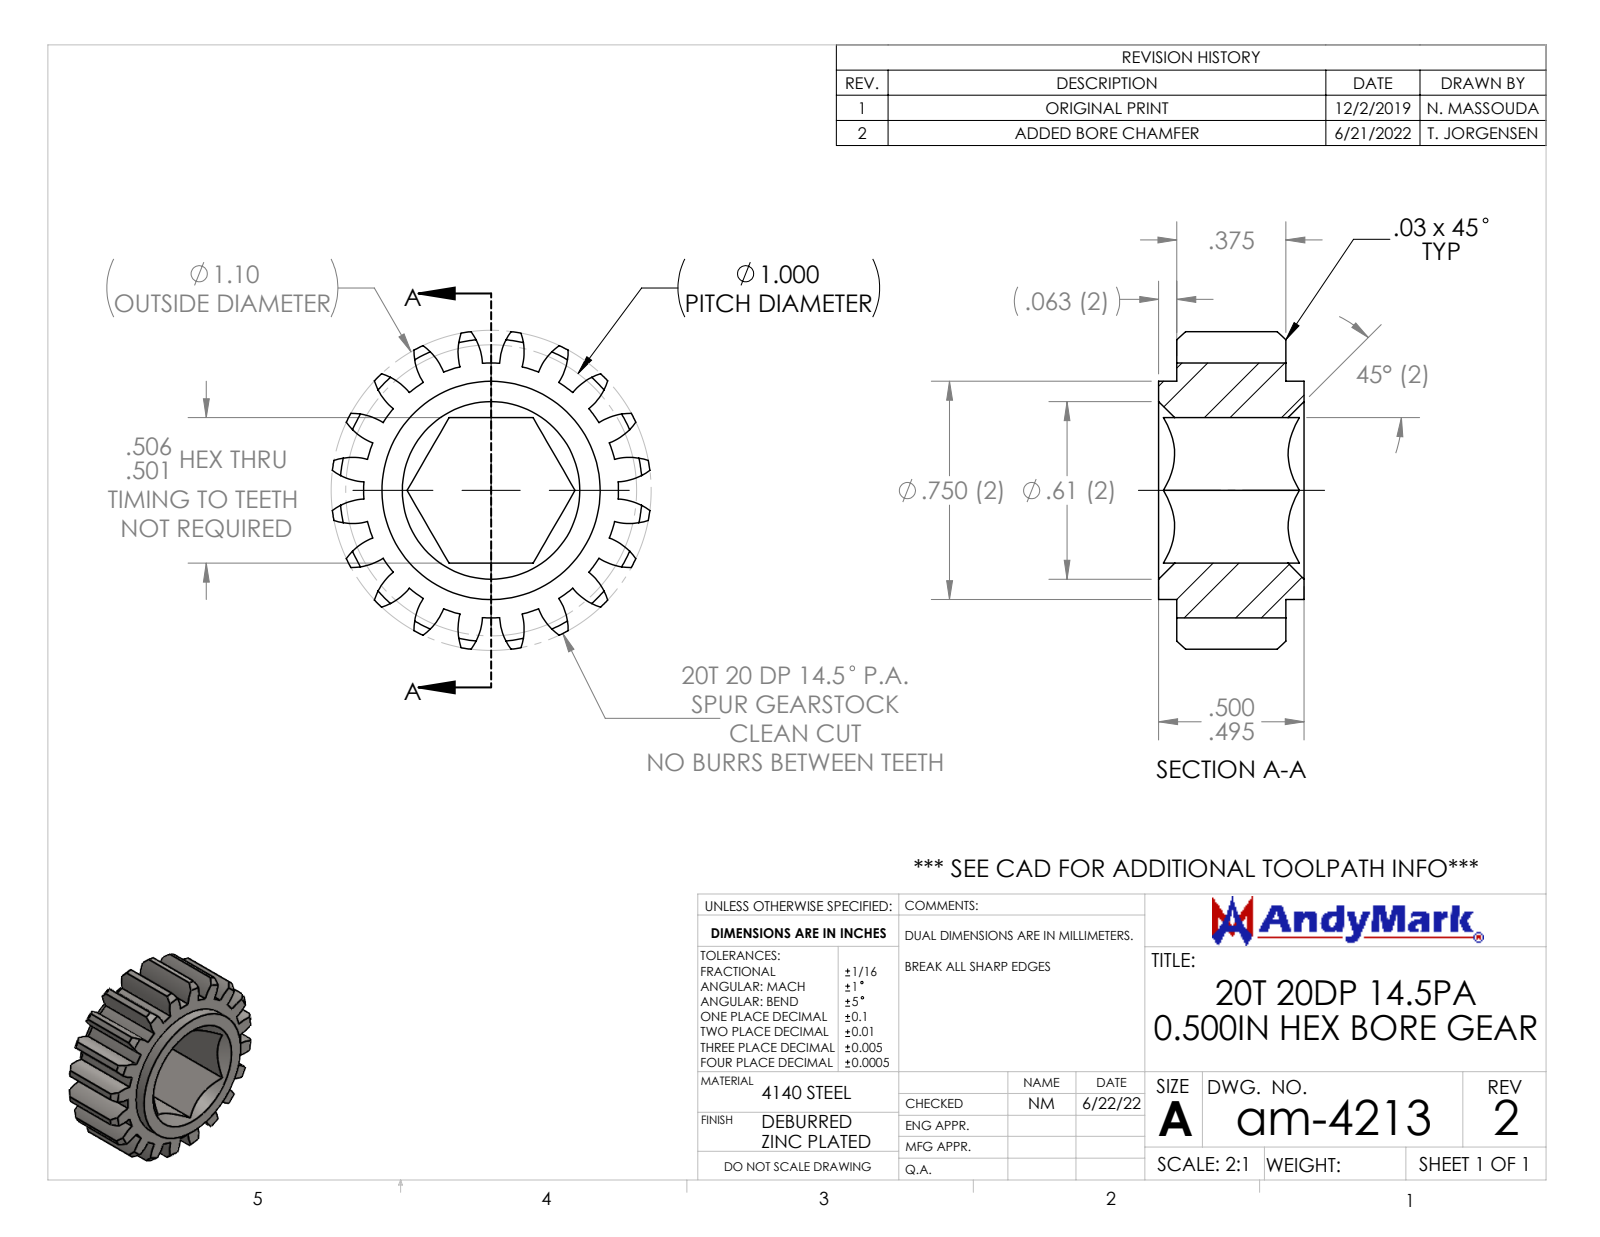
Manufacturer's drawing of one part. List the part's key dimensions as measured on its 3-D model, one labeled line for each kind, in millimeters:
Part name (STEP PRODUCT): am-4213 20T 20DP 500hex 375 FW
STEP written by: SolidWorks 2021 (CONFIG_CONTROL_DESIGN)
Units: millimetres
Bodies: 1 solid, 143 faces (10 planar, 89 cylindrical, 44 other)
Overall size (bounding box): 27.7 × 27.7 × 12.7
Volume: 3 700 mm³ · Surface area: 2 943 mm²
Round bosses / shafts (diameter × count): ⌀19.1 ×1
Partial cylindrical surfaces — rounded edges, fillets, slot ends (radius × count): R5.1 ×40, R11.1 ×1, R14 ×1
Main face-to-face distances: 12.7, 9.5, 11.1, 1.6, 1.6, 11.1
